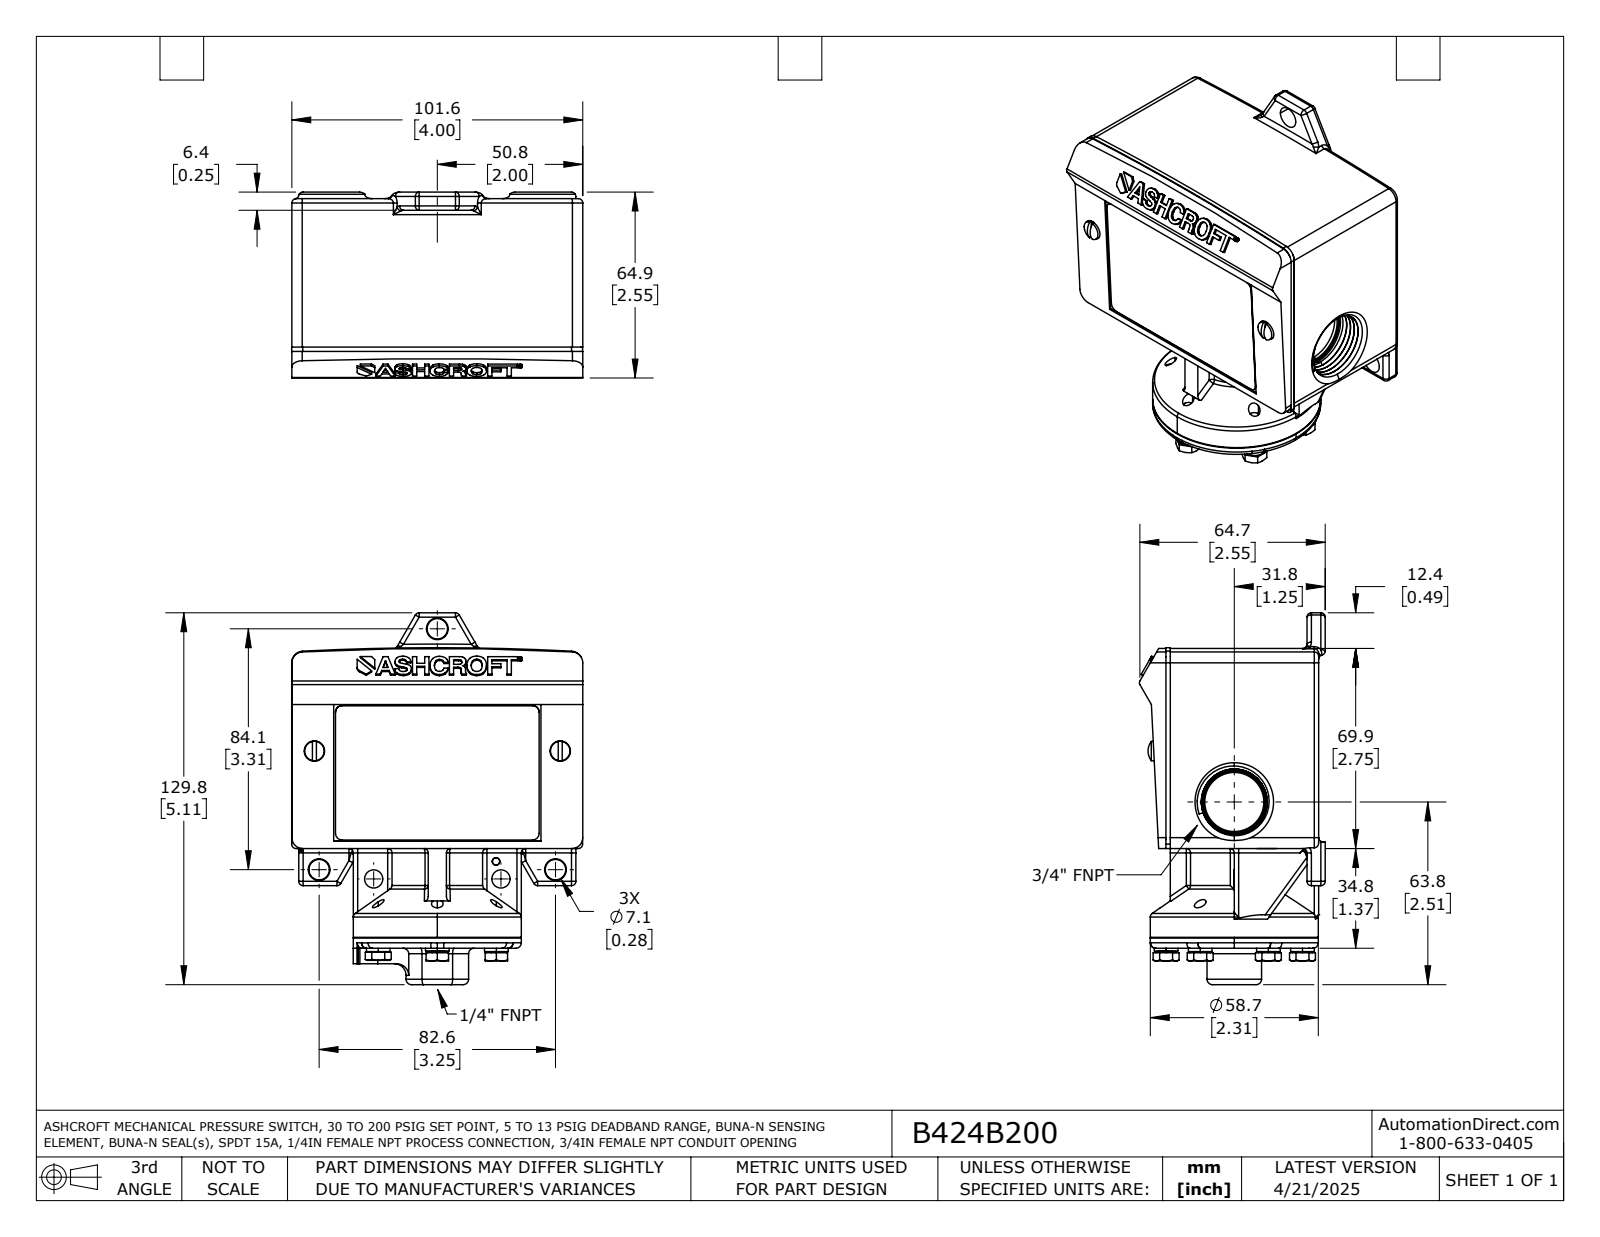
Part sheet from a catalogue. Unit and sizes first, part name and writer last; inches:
Units: inches
Overall size (bounding box): 5.111 × 4.003 × 2.555
Round holes (diameter × count): ⌀0.161 ×6, ⌀0.192 ×5, ⌀0.209 ×5, ⌀0.187 ×4, ⌀0.28 ×2, ⌀0.455 ×1, ⌀0.812 ×1
Round bosses / shafts (diameter × count): ⌀0.325 ×6, ⌀0.278 ×6, ⌀0.19 ×5, ⌀0.27 ×2, ⌀0.25 ×2, ⌀2.31 ×1
Partial cylindrical surfaces — rounded edges, fillets, slot ends (radius × count): R0.06 ×92, R0.03 ×5, R0.075 ×4, R0.09 ×4, R0.15 ×4, R0.01 ×2, R0.094 ×2, R0.16 ×2
Main face-to-face distances: 4, 0.015, 1.37, 0.09, 3.91, 0.44, 3.56, 3.47, 0.35, 0.845
Hole centre spacings: 0.937, 1.624, 1.875, 0.938, 3.38
Volume: 28.57 in³ · Surface area: 84.51 in²
Bodies: 2 solids, 1259 faces (345 planar, 472 cylindrical, 442 other)
Part name (STEP PRODUCT): B424B200
STEP written by: SolidWorks 2021 (AUTOMOTIVE_DESIGN)
